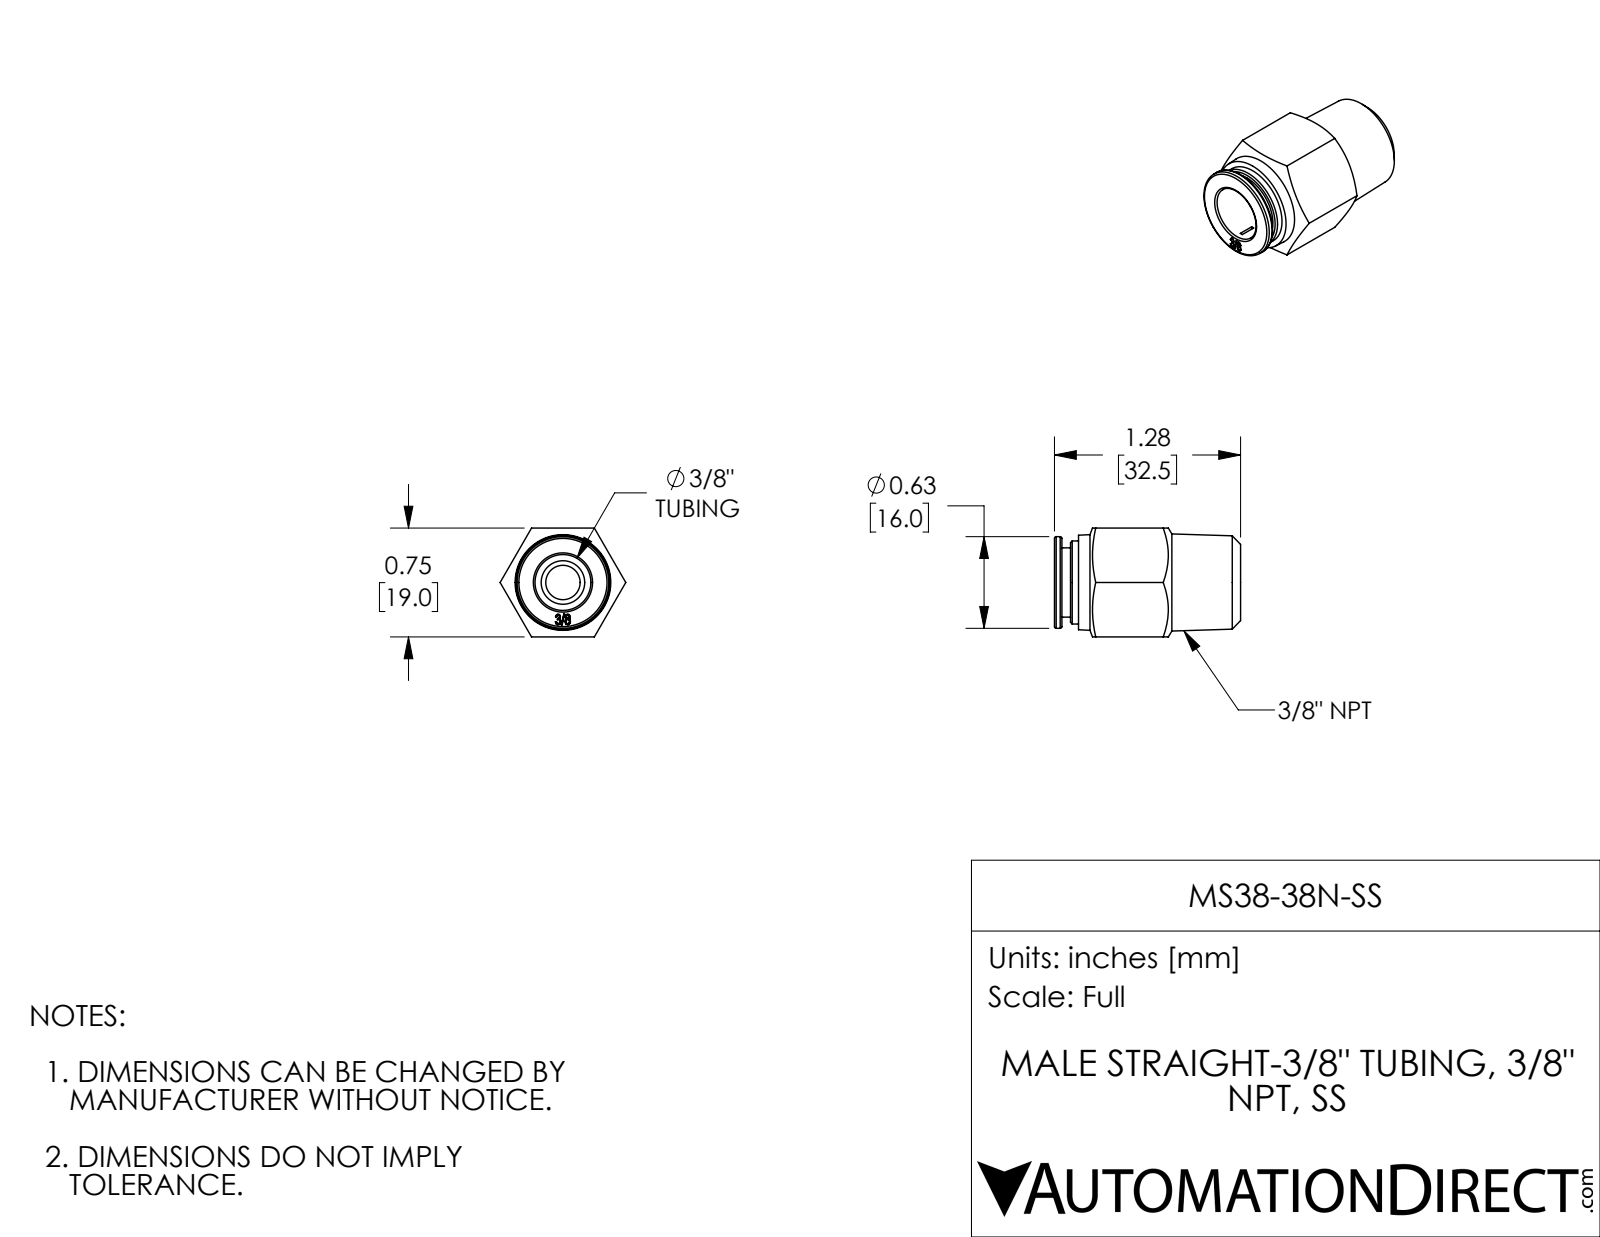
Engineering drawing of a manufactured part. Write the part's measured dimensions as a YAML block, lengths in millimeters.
part_name: "MS38-38N-SS"
step_written_by: "SolidWorks 2017 (AUTOMOTIVE_DESIGN)"
units: millimeters
bodies: {solids: 1, faces: 91, planar: 31, cylindrical: 10, other: 50}
overall_size: [32.5, 21.9, 19]
volume: 6160
surface_area: 3368
round_holes:
  - {diameter: 6, count: 1}
  - {diameter: 9.8, count: 1}
round_bosses_or_shafts:
  - {diameter: 16, count: 1}
  - {diameter: 14.5, count: 1}
  - {diameter: 12.1, count: 1}
face_to_face_distances: [19, 32.5, 31.2, 1.3, 28.3, 2.9, 4.2, 12.7, 15.6, 18.5]
